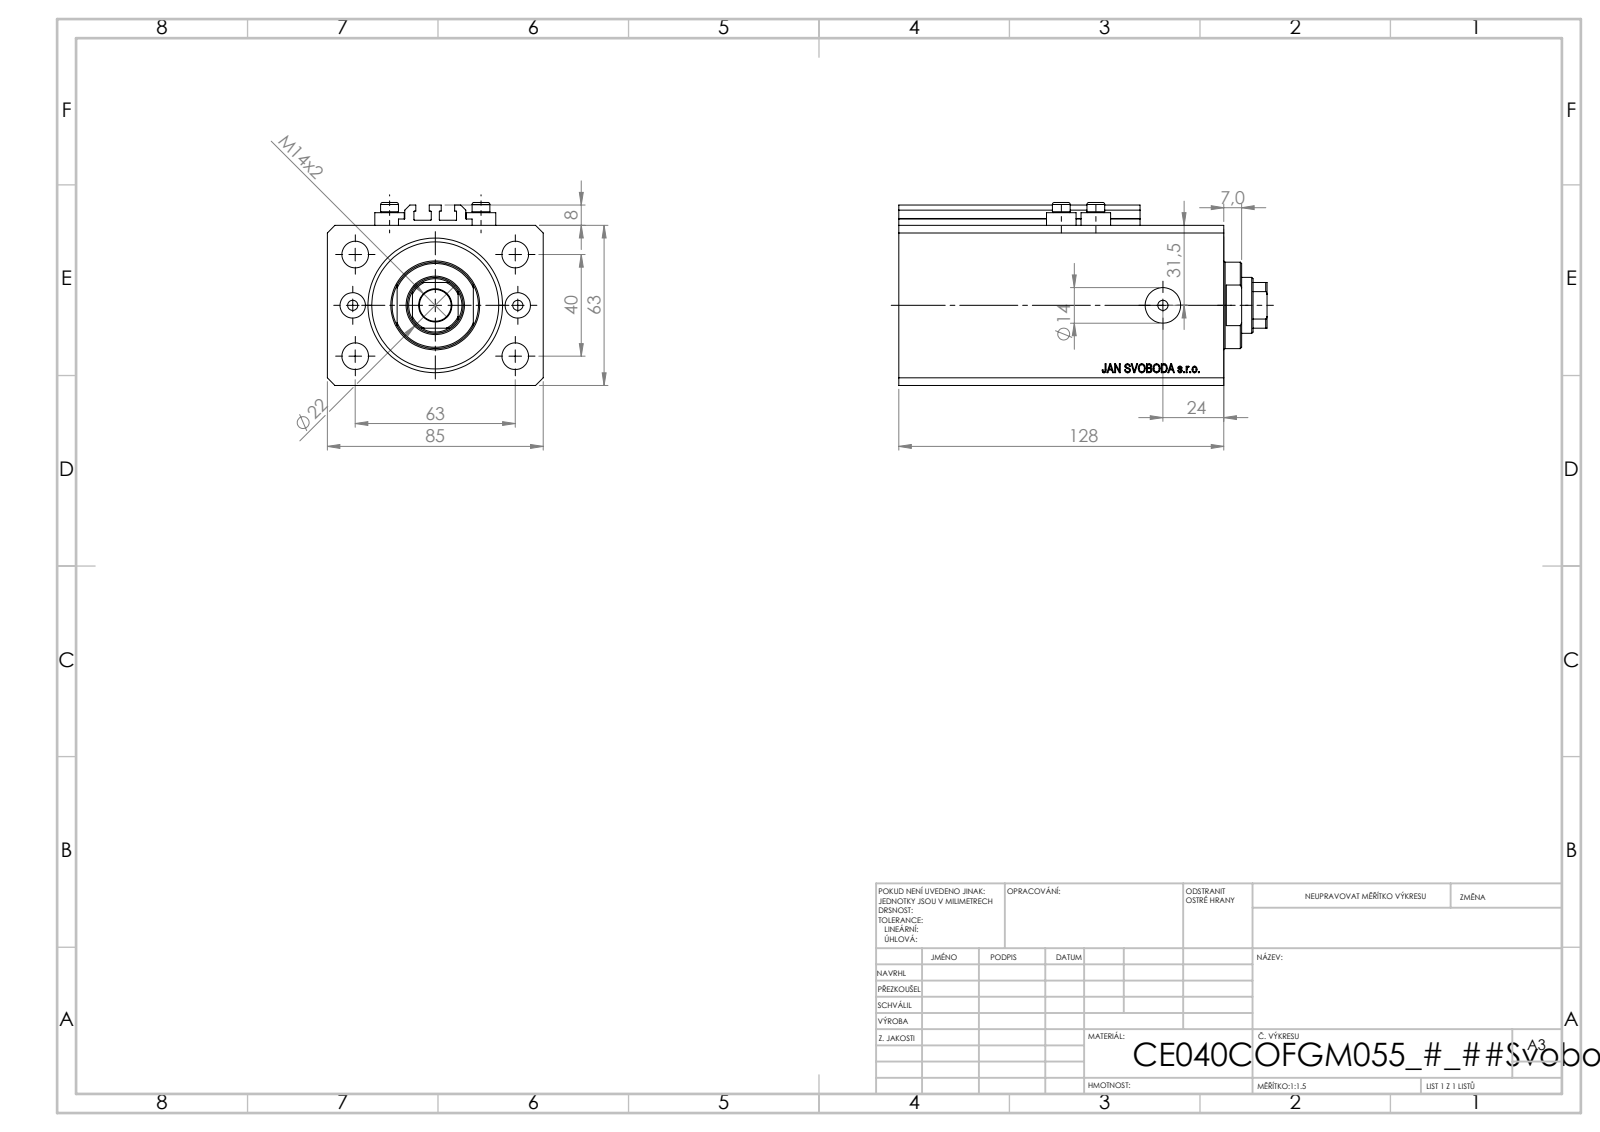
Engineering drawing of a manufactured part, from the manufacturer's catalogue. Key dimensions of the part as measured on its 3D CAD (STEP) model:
Part name (STEP PRODUCT): V250CE_VC_C; V250CE_C_Body; ALLEN BOLT V250CE; V250CE_C_VCP
STEP written by: SolidWorks 2019 (CONFIG_CONTROL_DESIGN)
Units: millimetres
Bodies: 8 solids, 1034 faces (504 planar, 86 cylindrical, 444 other)
Overall size (bounding box): 145 × 85 × 72
Volume: 608 545 mm³ · Surface area: 117 270 mm²
Round holes (diameter × count): ⌀4 ×8, ⌀10.5 ×4, ⌀10 ×2, ⌀14 ×2, ⌀12.5 ×1, ⌀22 ×1, ⌀40 ×1, ⌀53 ×1
Round bosses / shafts (diameter × count): ⌀11.6 ×4, ⌀7 ×4, ⌀34 ×1
Partial cylindrical surfaces — rounded edges, fillets, slot ends (radius × count): R0.2 ×10, R10.5 ×1
Main face-to-face distances: 63, 85, 128, 17, 111, 11.4, 99.6, 116.6, 2.5, 10
Hole centre spacings: 20.02, 37.31, 67.05, 13.6, 32.5, 36, 38.48, 40
